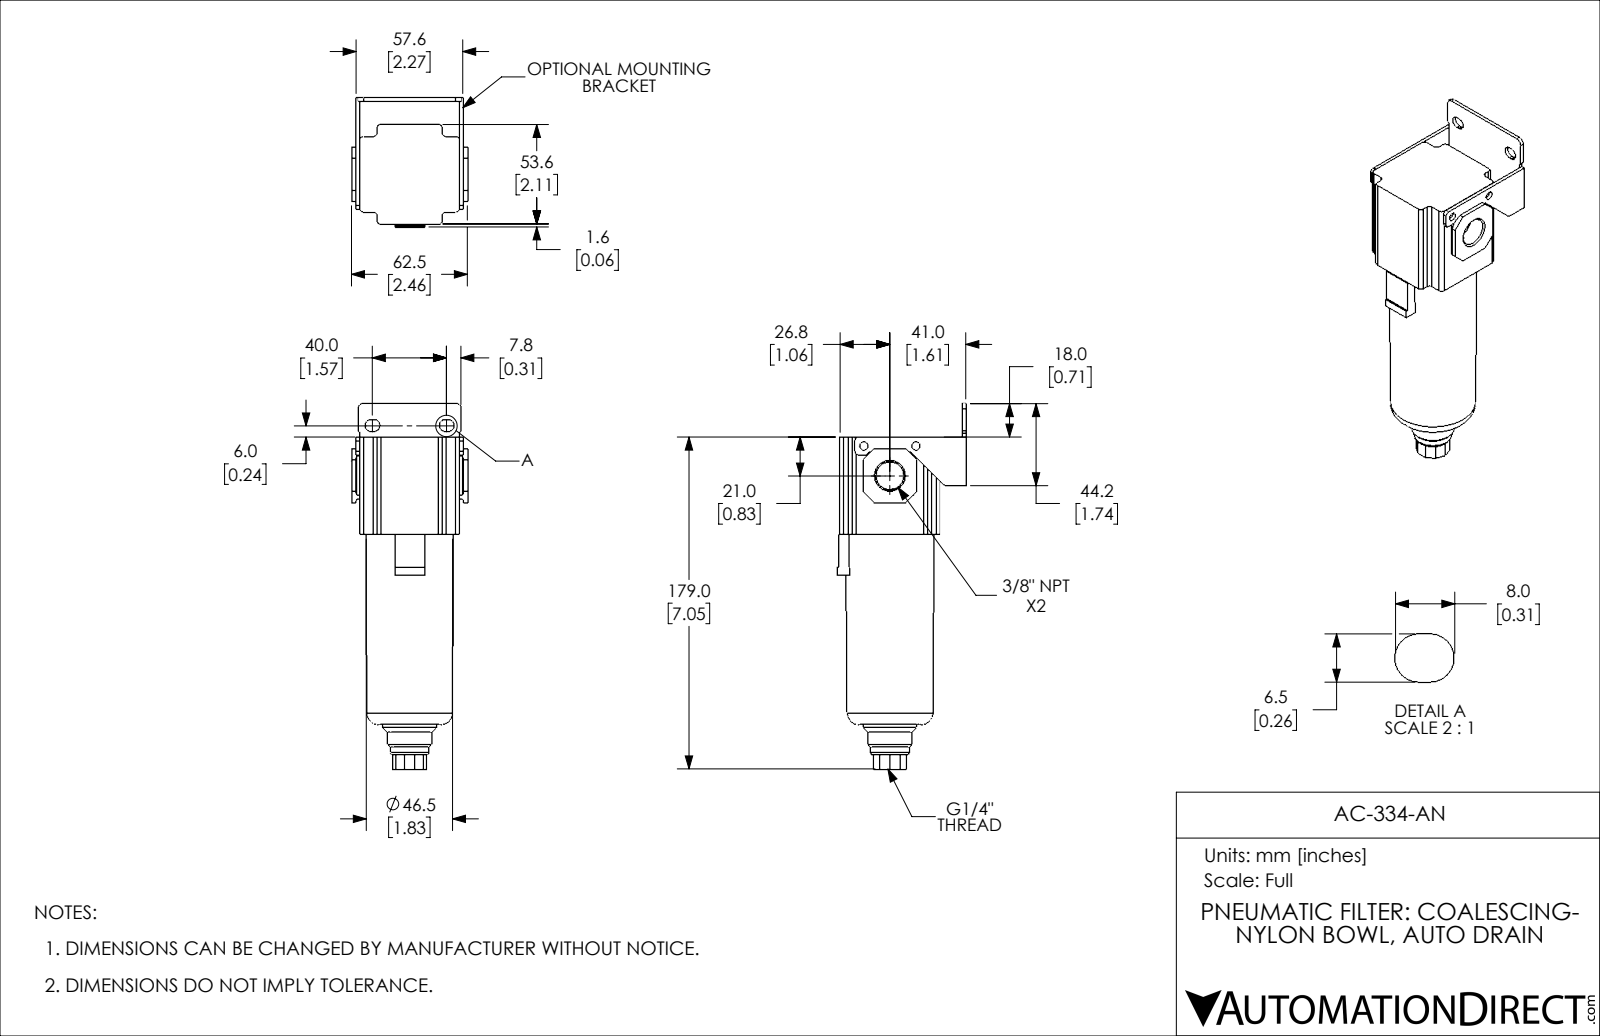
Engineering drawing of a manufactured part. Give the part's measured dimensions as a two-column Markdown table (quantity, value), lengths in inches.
| quantity | value |
| --- | --- |
| part name | AC-334-AN |
| STEP written by | SolidWorks 2018 (AUTOMOTIVE_DESIGN) |
| units | inches |
| bodies | 1 solid, 173 faces (109 planar, 48 cylindrical, 16 other) |
| overall size | 7.756 × 2.733 × 2.461 |
| volume | 19.92 in³ |
| surface area | 65.58 in² |
| round holes (diameter × count) | 0.177 × 2, 0.451 × 1, 0.589 × 1 |
| round bosses / shafts (diameter × count) | 1.102 × 1, 0.906 × 1, 0.787 × 1 |
| partial cylindrical surfaces (radius × count) | 0.079 × 15, 0.128 × 4, 0.039 × 2, 0.118 × 2 |
| main face-to-face distances | 0.079, 2.11, 2.189, 0.559, 2.669, 0.48, 2.591, 2.067, 0.258, 1.852 |
| hole center spacings | 0.837, 1.102 |
